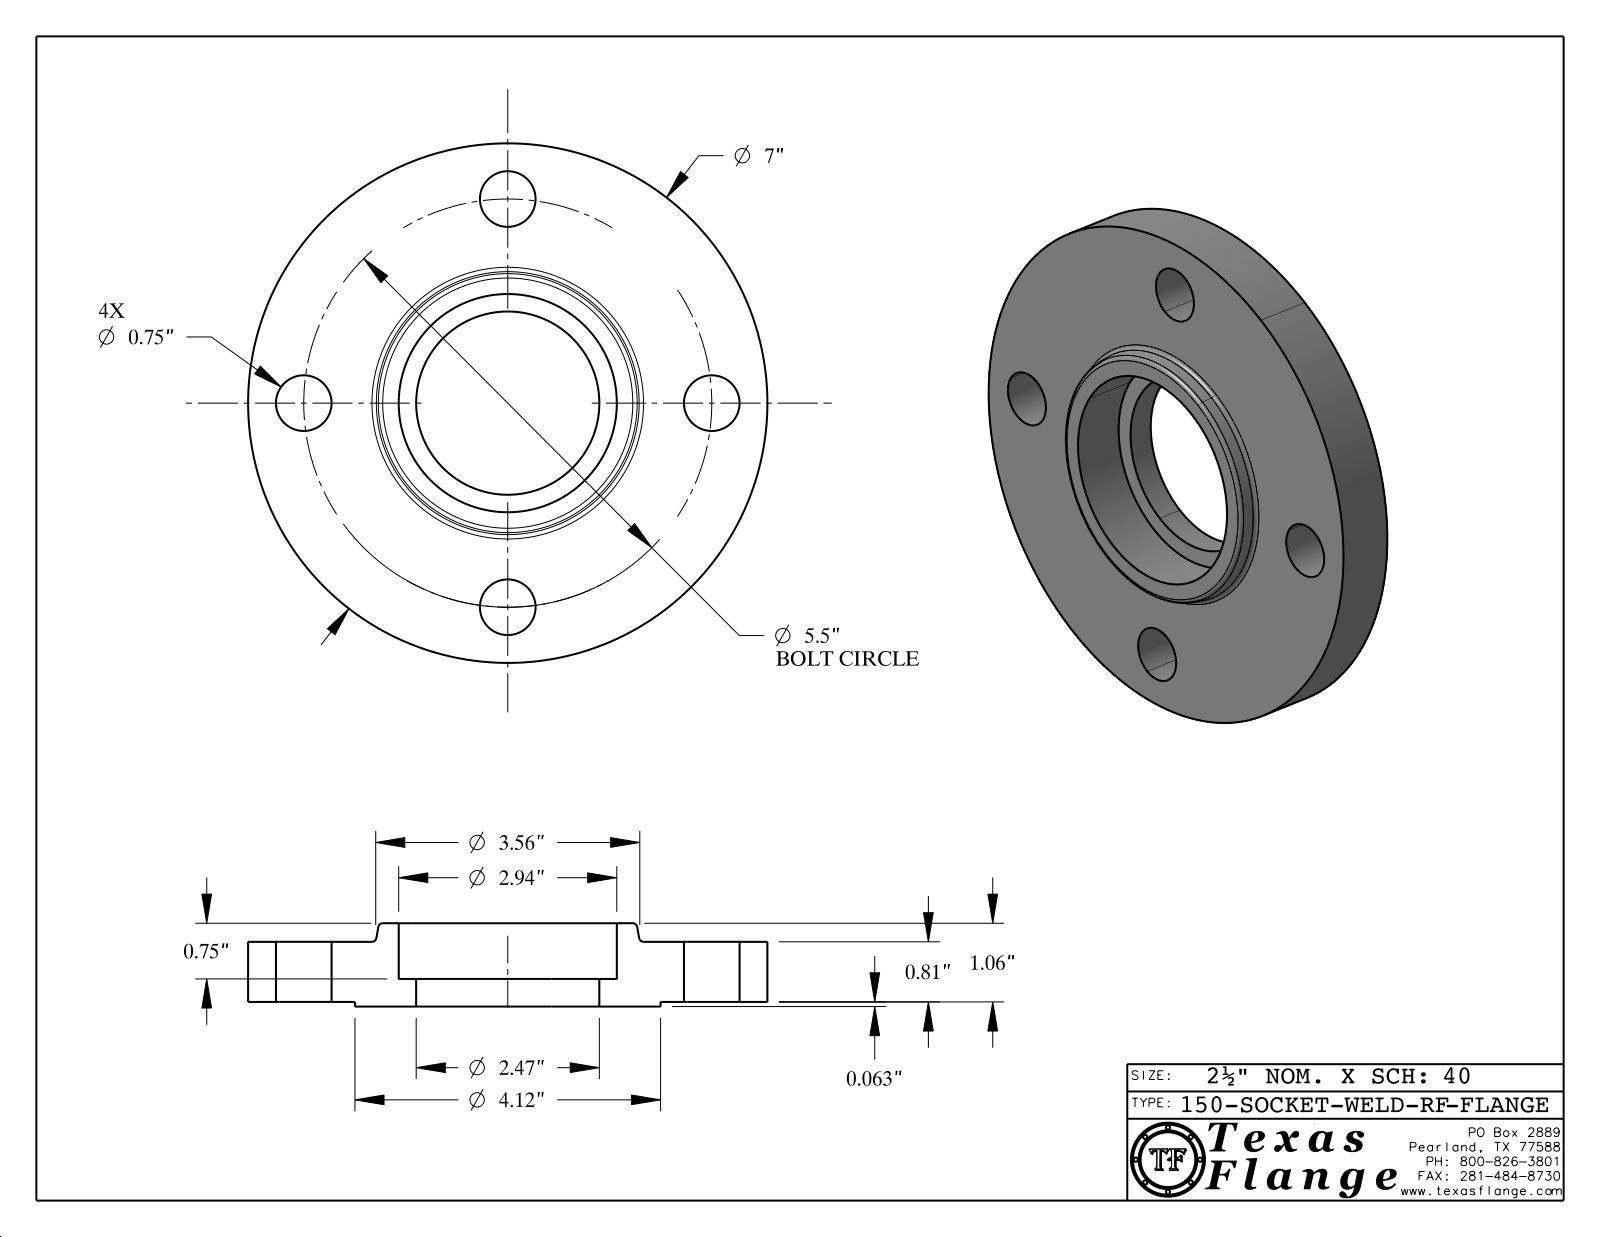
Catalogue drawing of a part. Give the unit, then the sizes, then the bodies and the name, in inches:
Units: inches
Overall size (bounding box): 7 × 7 × 1.123
Round holes (diameter × count): ⌀0.75 ×4, ⌀0.495 ×1, ⌀2.469 ×1, ⌀2.94 ×1
Round bosses / shafts (diameter × count): ⌀0.03 ×8, ⌀7 ×1, ⌀4.12 ×1, ⌀0.39 ×1
Main face-to-face distances: 0.81, 0.063, 0.872, 1.122, 1.06, 0.25, 0.372, 0.31, 0.5, 0.75
Hole centre spacings: 2.75, 3.889, 2.105, 5.081, 5.5
Volume: 26.13 in³ · Surface area: 102 in²
Bodies: 1 solid, 412 faces (370 planar, 36 cylindrical, 6 other)
Part name (STEP PRODUCT): 150-SOCKET-WELD-RF
STEP written by: CATIA V5 STEP AP214 (AUTOMOTIVE_DESIGN)
